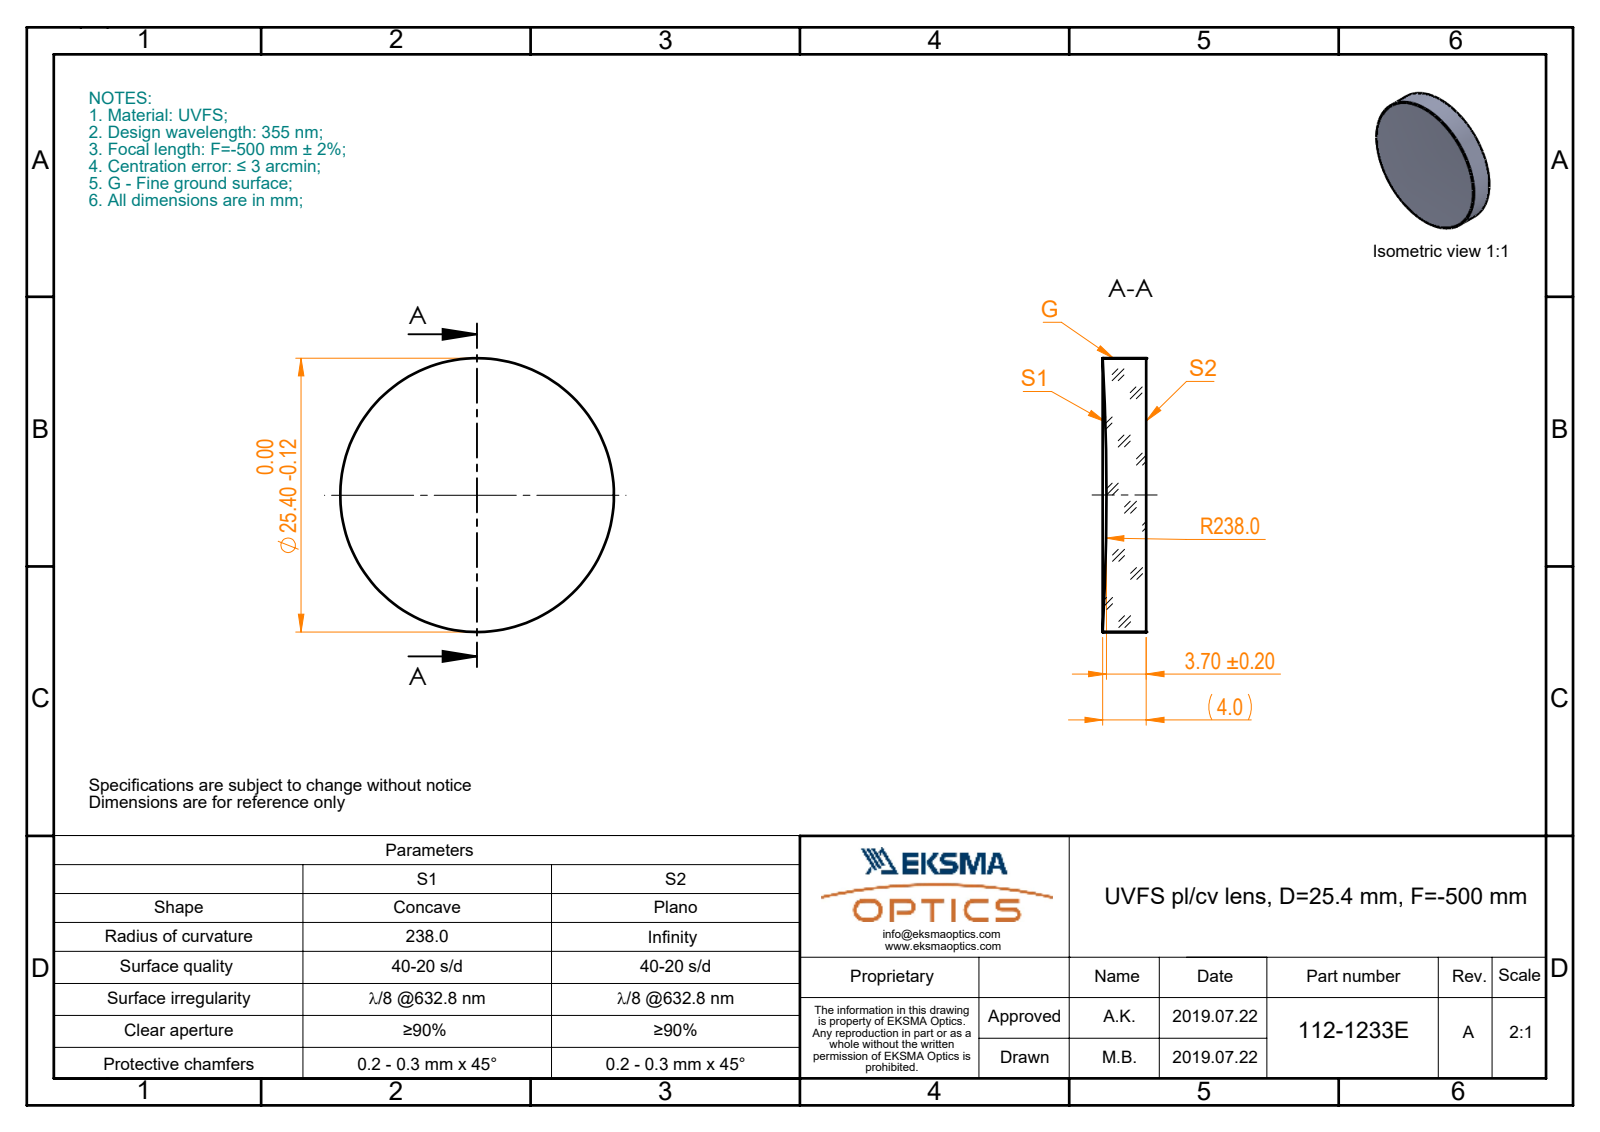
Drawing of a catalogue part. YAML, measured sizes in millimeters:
part_name: "112-1233E UVFS pl-cv 25.4 F-500"
step_written_by: "SolidWorks 2017 (CONFIG_CONTROL_DESIGN)"
units: millimeters
bodies: {solids: 1, faces: 5, planar: 1, cylindrical: 2, other: 2}
overall_size: [25.4, 25.4, 4.04]
volume: 1961
surface_area: 1336
round_bosses_or_shafts:
  - {diameter: 25.4, count: 1}
